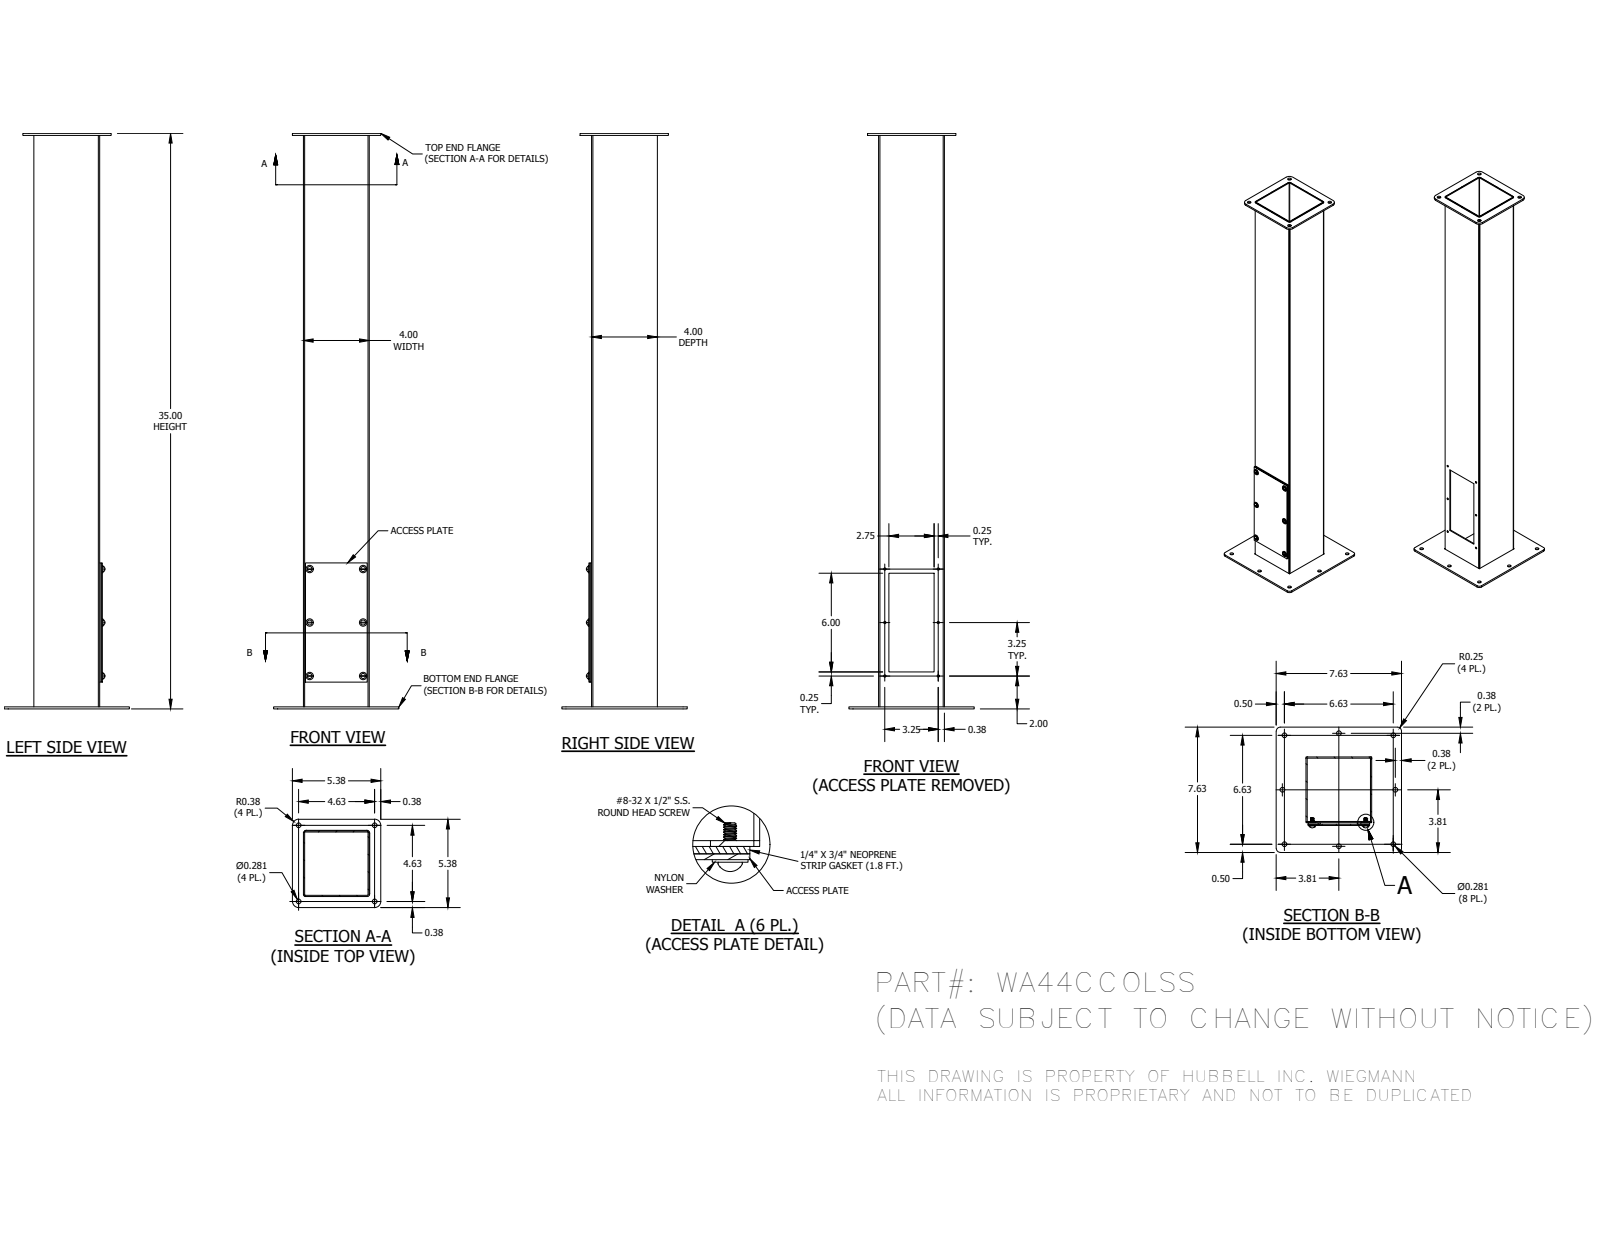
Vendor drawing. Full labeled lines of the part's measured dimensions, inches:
Part name (STEP PRODUCT): WA44CCOLSSFRONT; WA44CCOLSSBLR; WA44CCOLSSBASERING; WA44CCOLSSCOVER (+5 more)
STEP written by: Autodesk Inventor 2016 (AUTOMOTIVE_DESIGN)
Units: inches
Bodies: 24 solids, 332 faces (202 planar, 94 cylindrical, 36 other)
Overall size (bounding box): 35 × 7.625 × 7.625
Volume: 49.08 in³ · Surface area: 1 279 in²
Round holes (diameter × count): ⌀0.281 ×12, ⌀0.14 ×6, ⌀0.25 ×6, ⌀0.278 ×6
Round bosses / shafts (diameter × count): ⌀0.453 ×6, ⌀0.309 ×6, ⌀0.164 ×6, ⌀0.123 ×6
Partial cylindrical surfaces — rounded edges, fillets, slot ends (radius × count): R0.089 ×6, R0.187 ×4, R0.25 ×4, R0.375 ×4, R0.031 ×2, R0.105 ×2
Main face-to-face distances: 0.074, 3.926, 4, 3.852, 4.094, 0.168, 0.125, 4.02, 0.094, 4.168
Hole centre spacings: 3.25, 3.315, 4.596, 7.519, 6.5, 4.625, 4.861, 6.625
